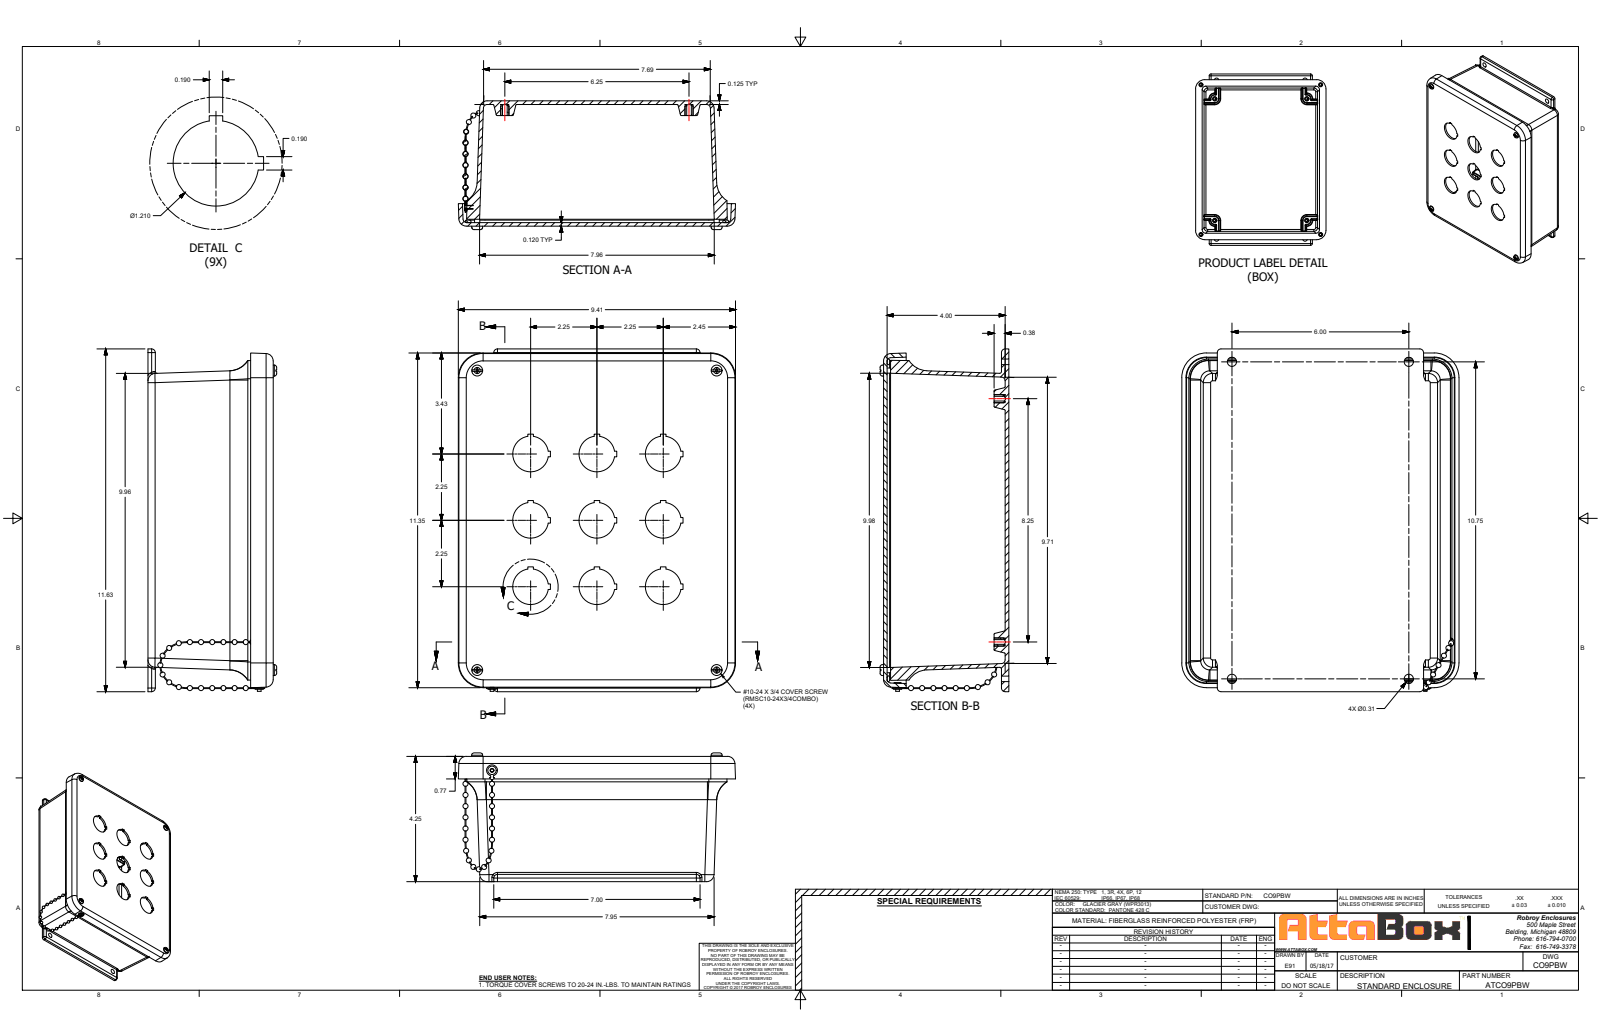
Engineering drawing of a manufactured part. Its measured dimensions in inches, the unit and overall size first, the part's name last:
Units: inches
Overall size (bounding box): 11.625 × 9.405 × 4.368
Round holes (diameter × count): ⌀1.21 ×9, ⌀0.159 ×8, ⌀0.219 ×4, ⌀0.25 ×4, ⌀0.281 ×4, ⌀0.313 ×4, ⌀0.104 ×2, ⌀0.126 ×2, ⌀0.14 ×2
Round bosses / shafts (diameter × count): ⌀0.27 ×8, ⌀0.371 ×4, ⌀0.177 ×4, ⌀0.283 ×2, ⌀0.125 ×2, ⌀0.029 ×2, ⌀0.37 ×1
Partial cylindrical surfaces — rounded edges, fillets, slot ends (radius × count): R0.031 ×36, R0.012 ×16, R0.125 ×16, R0.25 ×12, R0.043 ×8, R0.314 ×4, R0.75 ×4, R0.031 ×2
Main face-to-face distances: 4.25, 0.126, 4.13, 0.12, 0.125, 4.005, 4.125, 4.015, 3.89, 0.115
Hole centre spacings: 2.25, 3.182, 5.031, 4.5, 1.104, 1.257, 1.337, 2.069
Volume: 55.57 in³ · Surface area: 751.7 in²
Bodies: 40 solids, 659 faces (243 planar, 217 cylindrical, 199 other)
Part name (STEP PRODUCT): CO9PBW
STEP written by: SolidWorks 2018 (AUTOMOTIVE_DESIGN)
